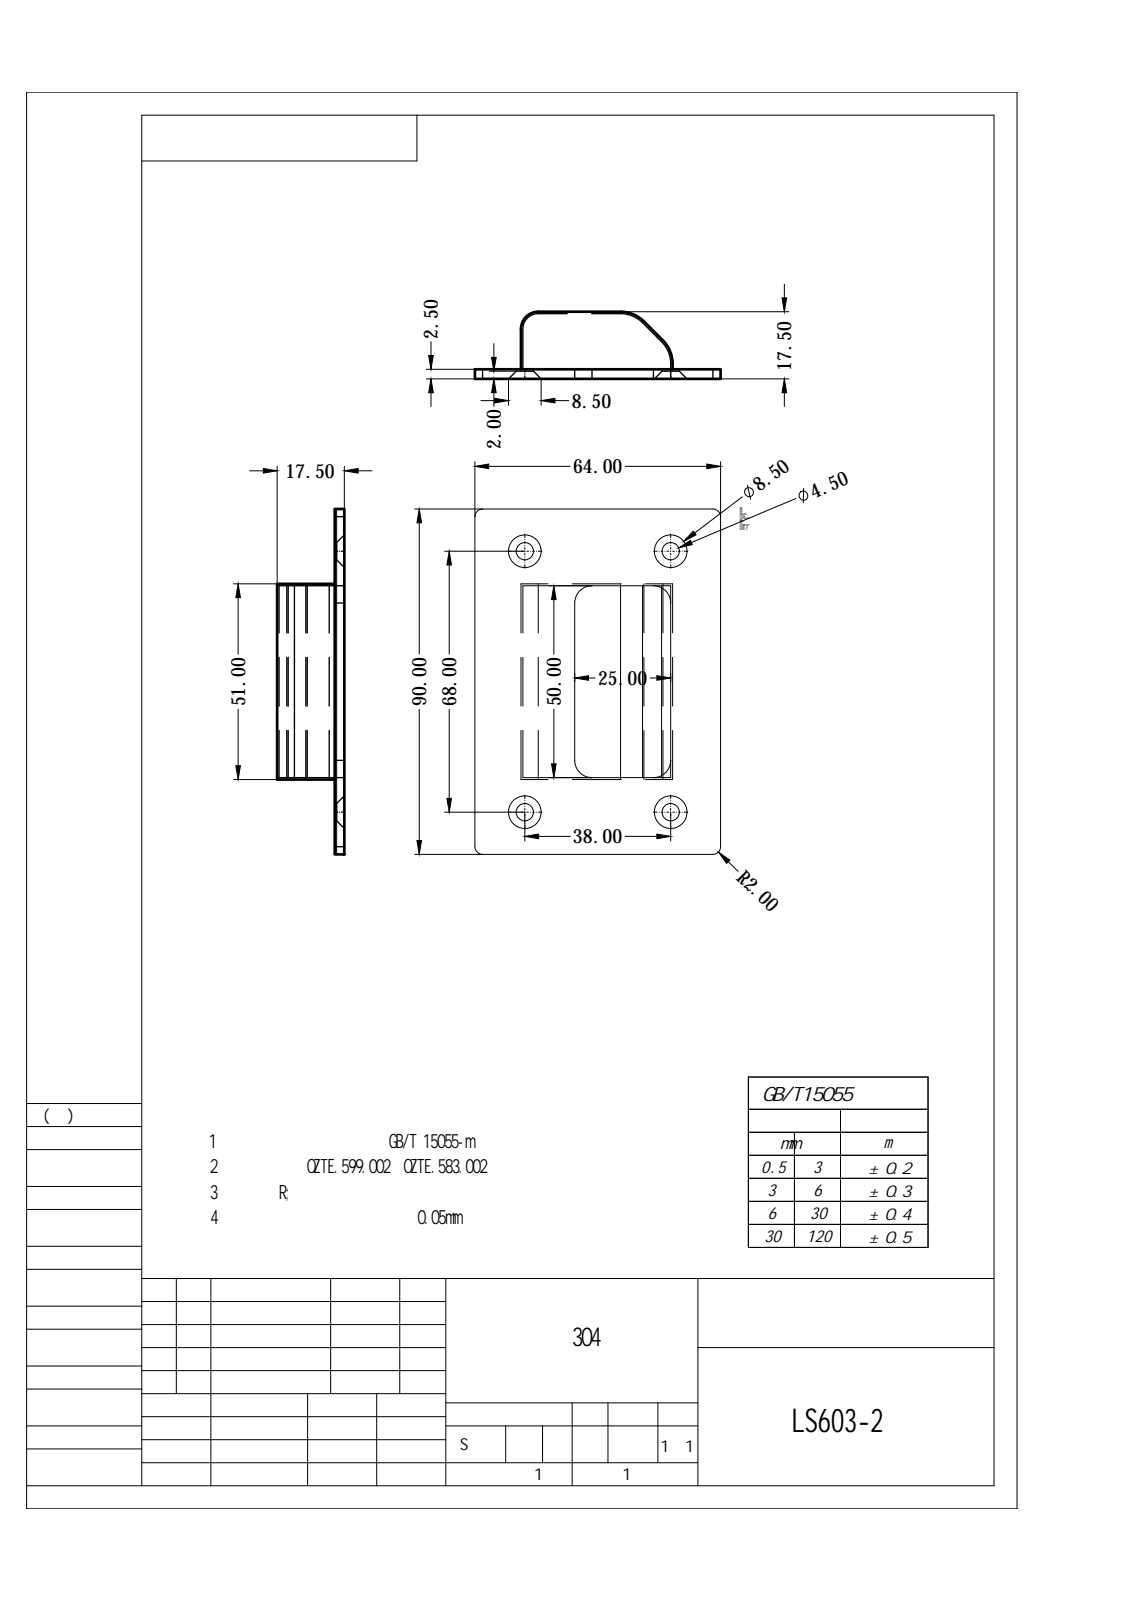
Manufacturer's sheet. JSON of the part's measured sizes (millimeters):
{"step_written_by": "Rhino 8.5 (CONFIG_CONTROL_DESIGN)", "units": "millimeters", "bodies": {"solids": 2, "faces": 106, "planar": 28, "cylindrical": 50, "other": 28}, "overall_size": [90, 64, 17.5], "volume_mm3": 12643, "surface_area_mm2": 25315, "round_holes": [[4.5, 4]], "partial_cylinders_radius": [[3, 8], [3.5, 8], [4.5, 5], [0.5, 4], [1, 4], [2, 4], [8.1, 2], [8.6, 2]], "face_to_face_distances": [0.5, 2, 2.5, 15, 15.5, 17.5, 14.5, 17, 50.5, 51], "hole_center_spacings": [38, 68, 77.9]}
